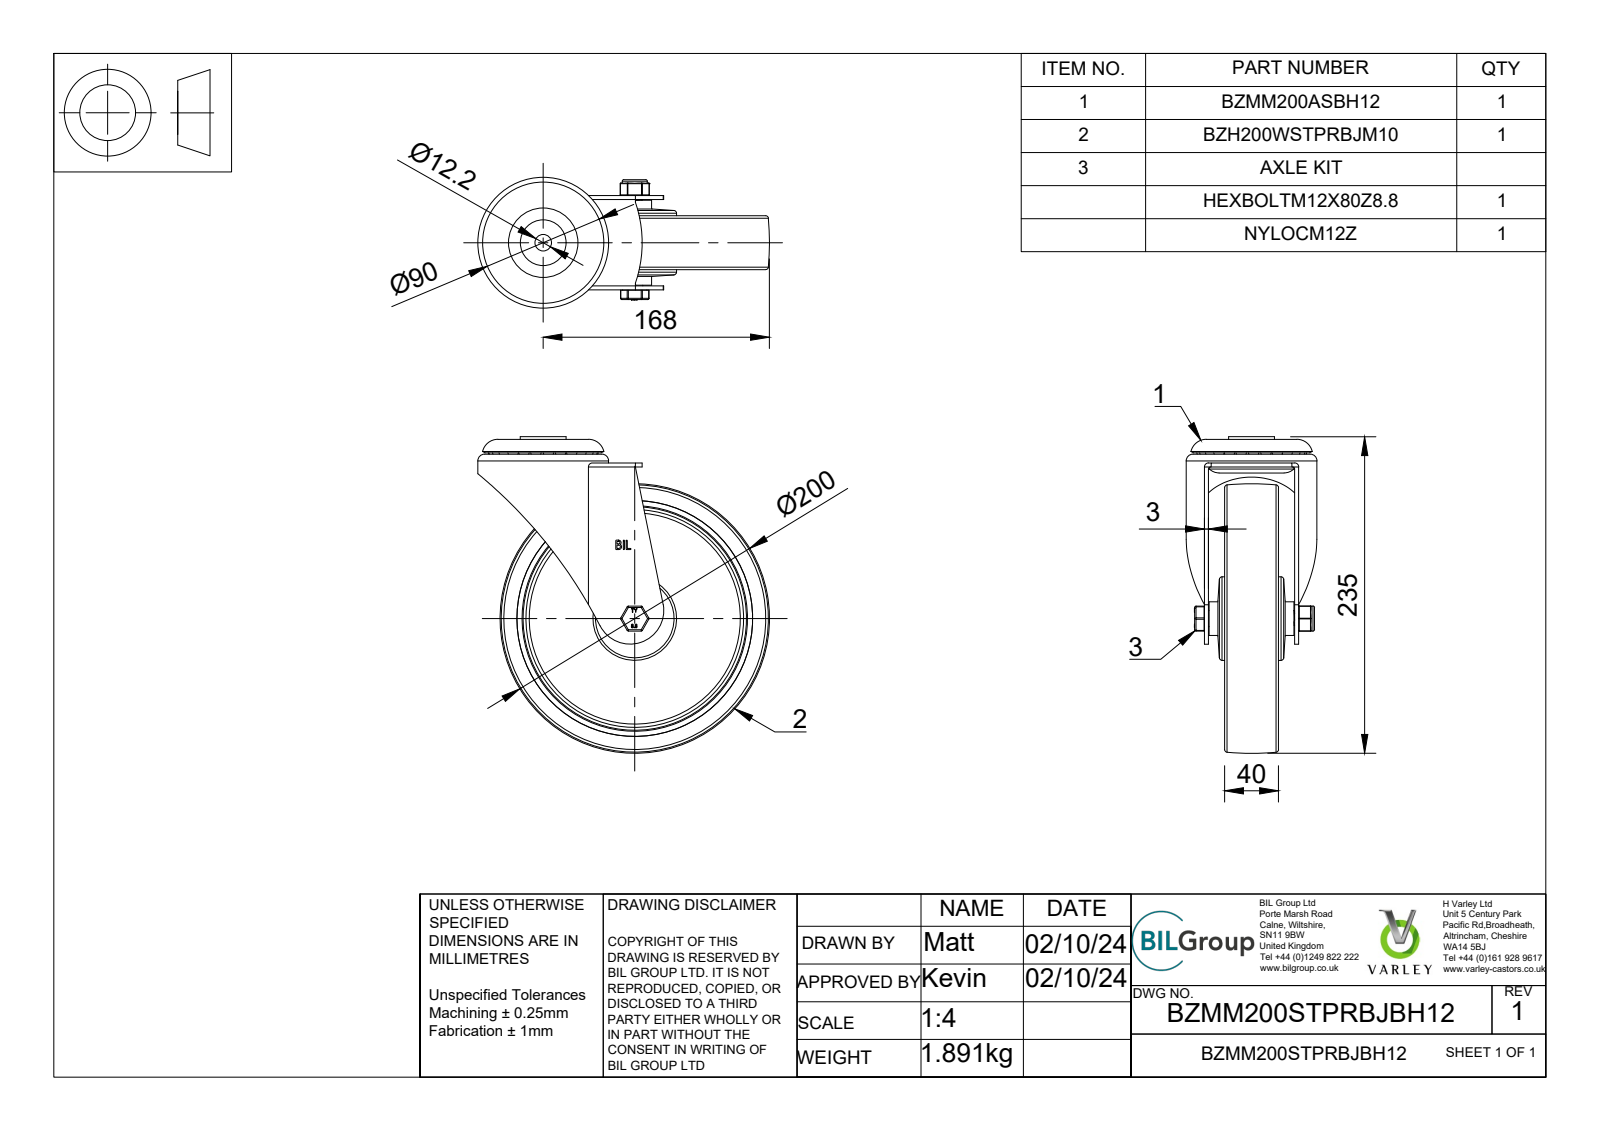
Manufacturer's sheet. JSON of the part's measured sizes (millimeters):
{"part_name": "BZMM200STPRBJBH12 v3; BZMM200ASBH12 - 64 v1; ZINC PLATED, PRESSED STEEL HEAD (1); ZINC PLATED, PRESSED STEEL HEAD Geometry (1) (+8 more)", "step_written_by": "Autodesk Translation Framework v13.20.0.188 (AUTOMOTIVE_DESIGN)", "units": "millimeters", "bodies": {"solids": 67, "faces": 757, "planar": 266, "cylindrical": 161, "other": 330}, "overall_size": [235, 216.5, 97], "volume_mm3": 769694, "surface_area_mm2": 294568, "round_holes": [[12, 1], [12.2, 1], [12.3, 1], [12.6, 1], [14, 1], [20, 1], [28.5, 1], [30.8, 1], [40.3, 1], [40.5, 1], [42, 1], [43, 1]], "round_bosses_or_shafts": [[97, 1], [63, 1], [62, 1], [56.5, 1], [48, 1], [40.8, 1], [39, 1], [34, 1]], "partial_cylinders_radius": [[0.5, 18], [1, 12], [1.5, 4], [3, 2], [16.5, 1], [19.5, 1], [25, 1], [92.5, 1]], "face_to_face_distances": [6.5, 16.75, 23.25, 3, 12, 15, 38.25, 28.75, 31.75, 55]}
